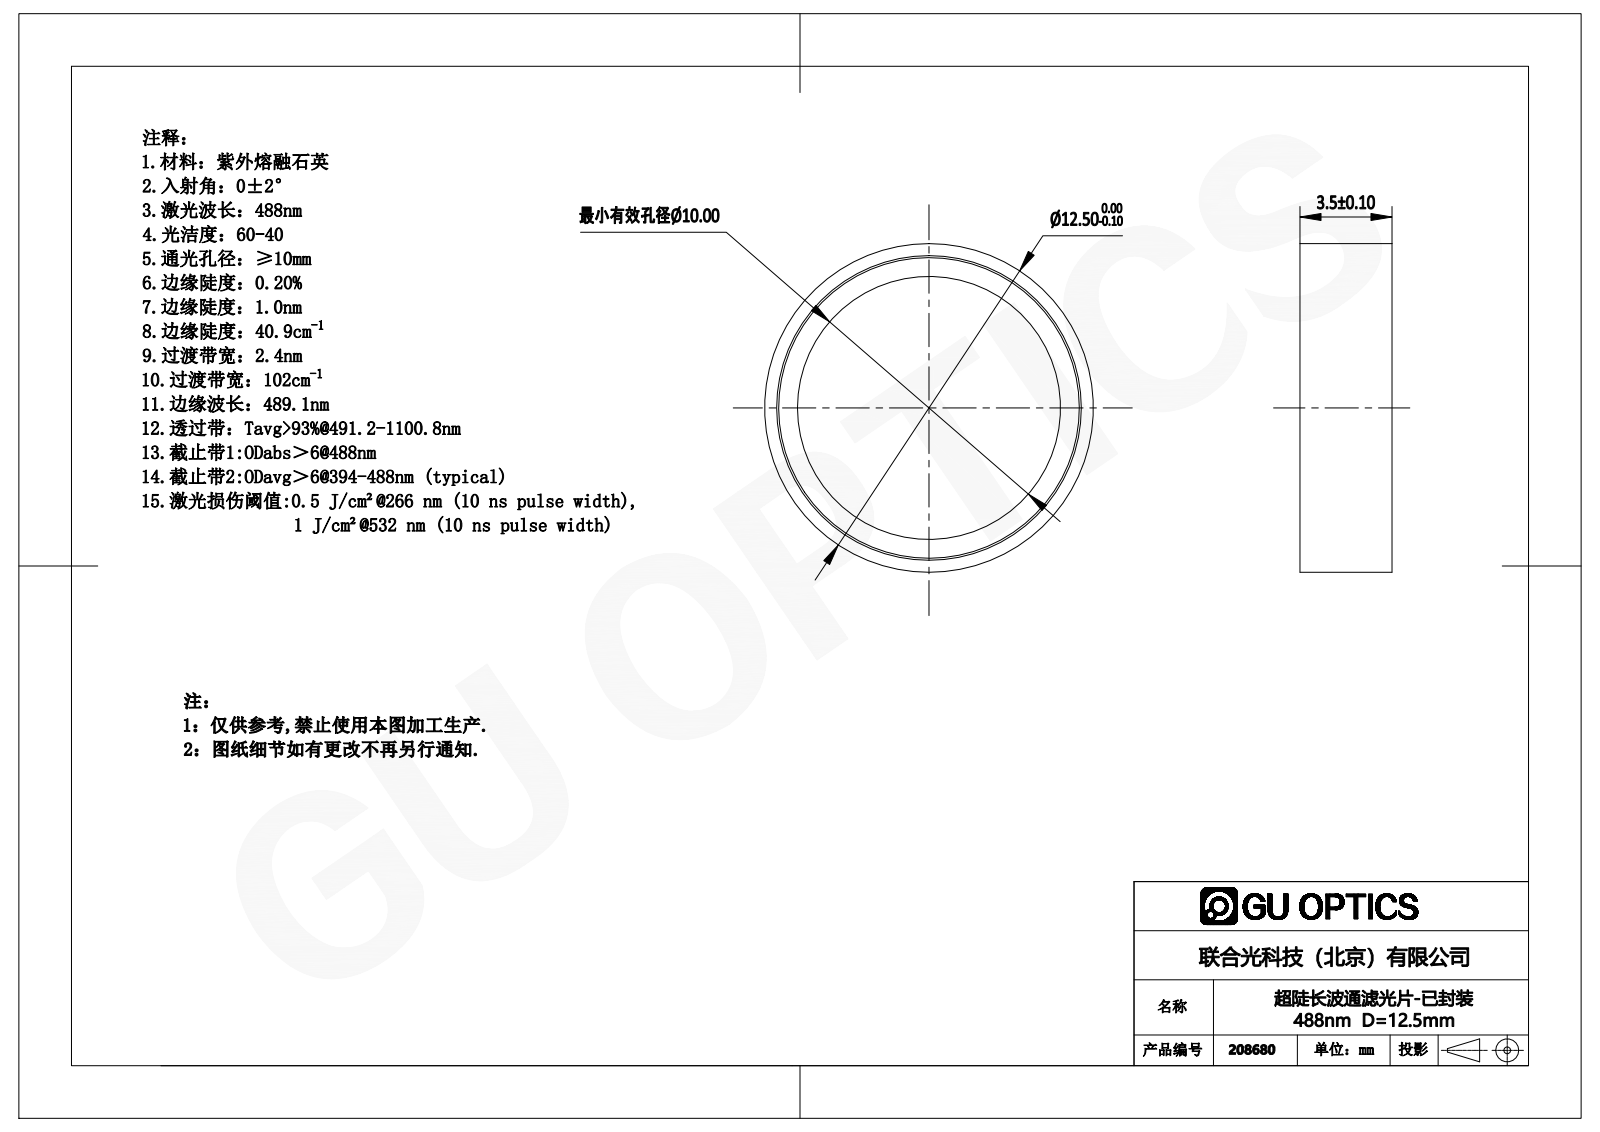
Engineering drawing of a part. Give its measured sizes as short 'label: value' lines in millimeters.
name: 208656
written by: SolidWorks 2016 (AUTOMOTIVE_DESIGN)
unit: mm
bodies: 3 solids, 22 faces (8 planar, 14 cylindrical, 0 other)
size: 12.5 × 12.5 × 3.5
volume: 291 mm³; area: 742 mm²
holes: 1× ⌀8.69, 1× ⌀10, 1× ⌀11.58, 1× ⌀11.71
bosses: 1× ⌀12.5, 1× ⌀11.43, 1× ⌀11.4
face distances: 2, 0.38, 2.38, 2.76, 3.5, 3.12, 1.12, 0.74, 0.69, 0.31
